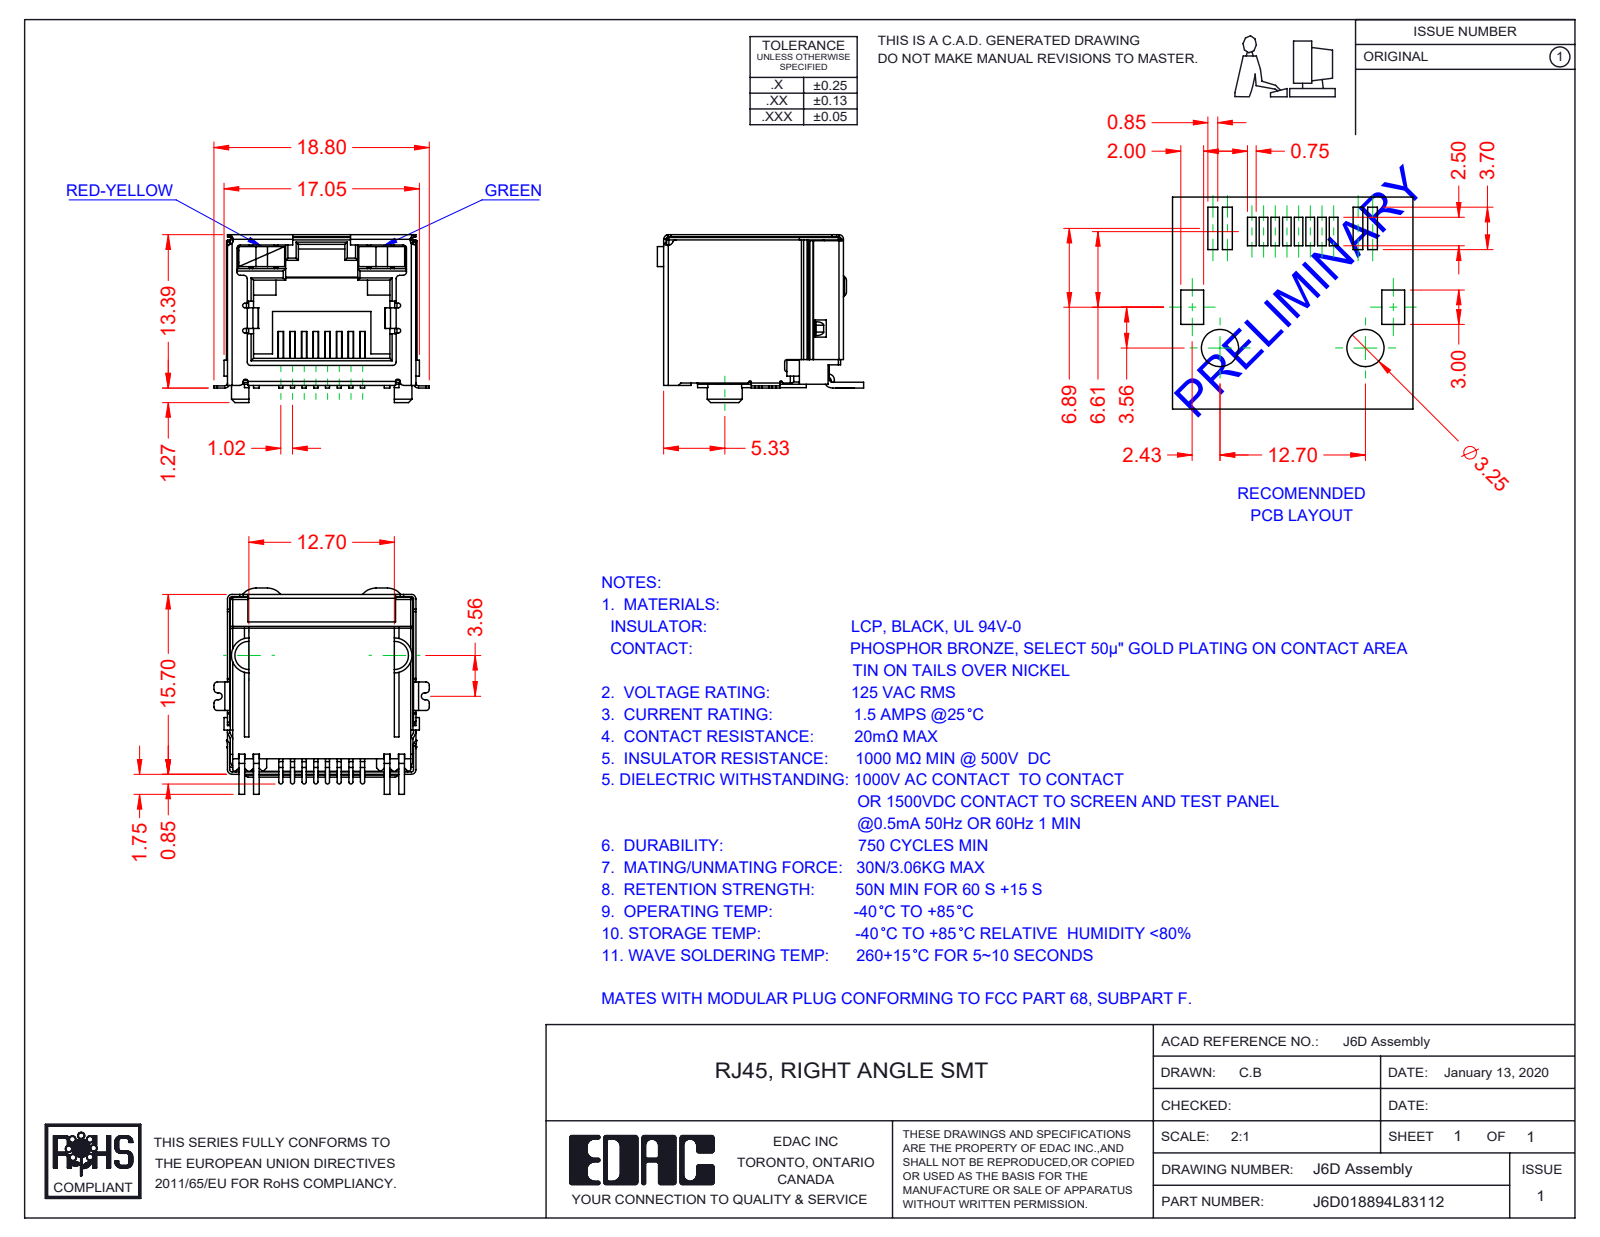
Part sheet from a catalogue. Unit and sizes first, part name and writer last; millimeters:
Units: millimetres
Overall size (bounding box): 18.8 × 18 × 14.65
Partial cylindrical surfaces — rounded edges, fillets, slot ends (radius × count): R0.3 ×39, R0.2 ×37, R0.4 ×16, R0.1 ×12, R0.15 ×8, R0.18 ×8, R0.5 ×6, R1.5 ×5
Main face-to-face distances: 16, 16.25, 16.2, 2.25, 1, 15.95, 16.05, 12.8, 0.45, 16.45
Volume: 1 804 mm³ · Surface area: 4 898 mm²
Bodies: 12 solids, 896 faces (645 planar, 218 cylindrical, 33 other)
Part name (STEP PRODUCT): 6D Insulator; 6D LED RH_3-Green; 6D LED LH_8-Red-Yellow; 6D Contacts (+2 more)
STEP written by: SolidWorks 2016 (CONFIG_CONTROL_DESIGN)
